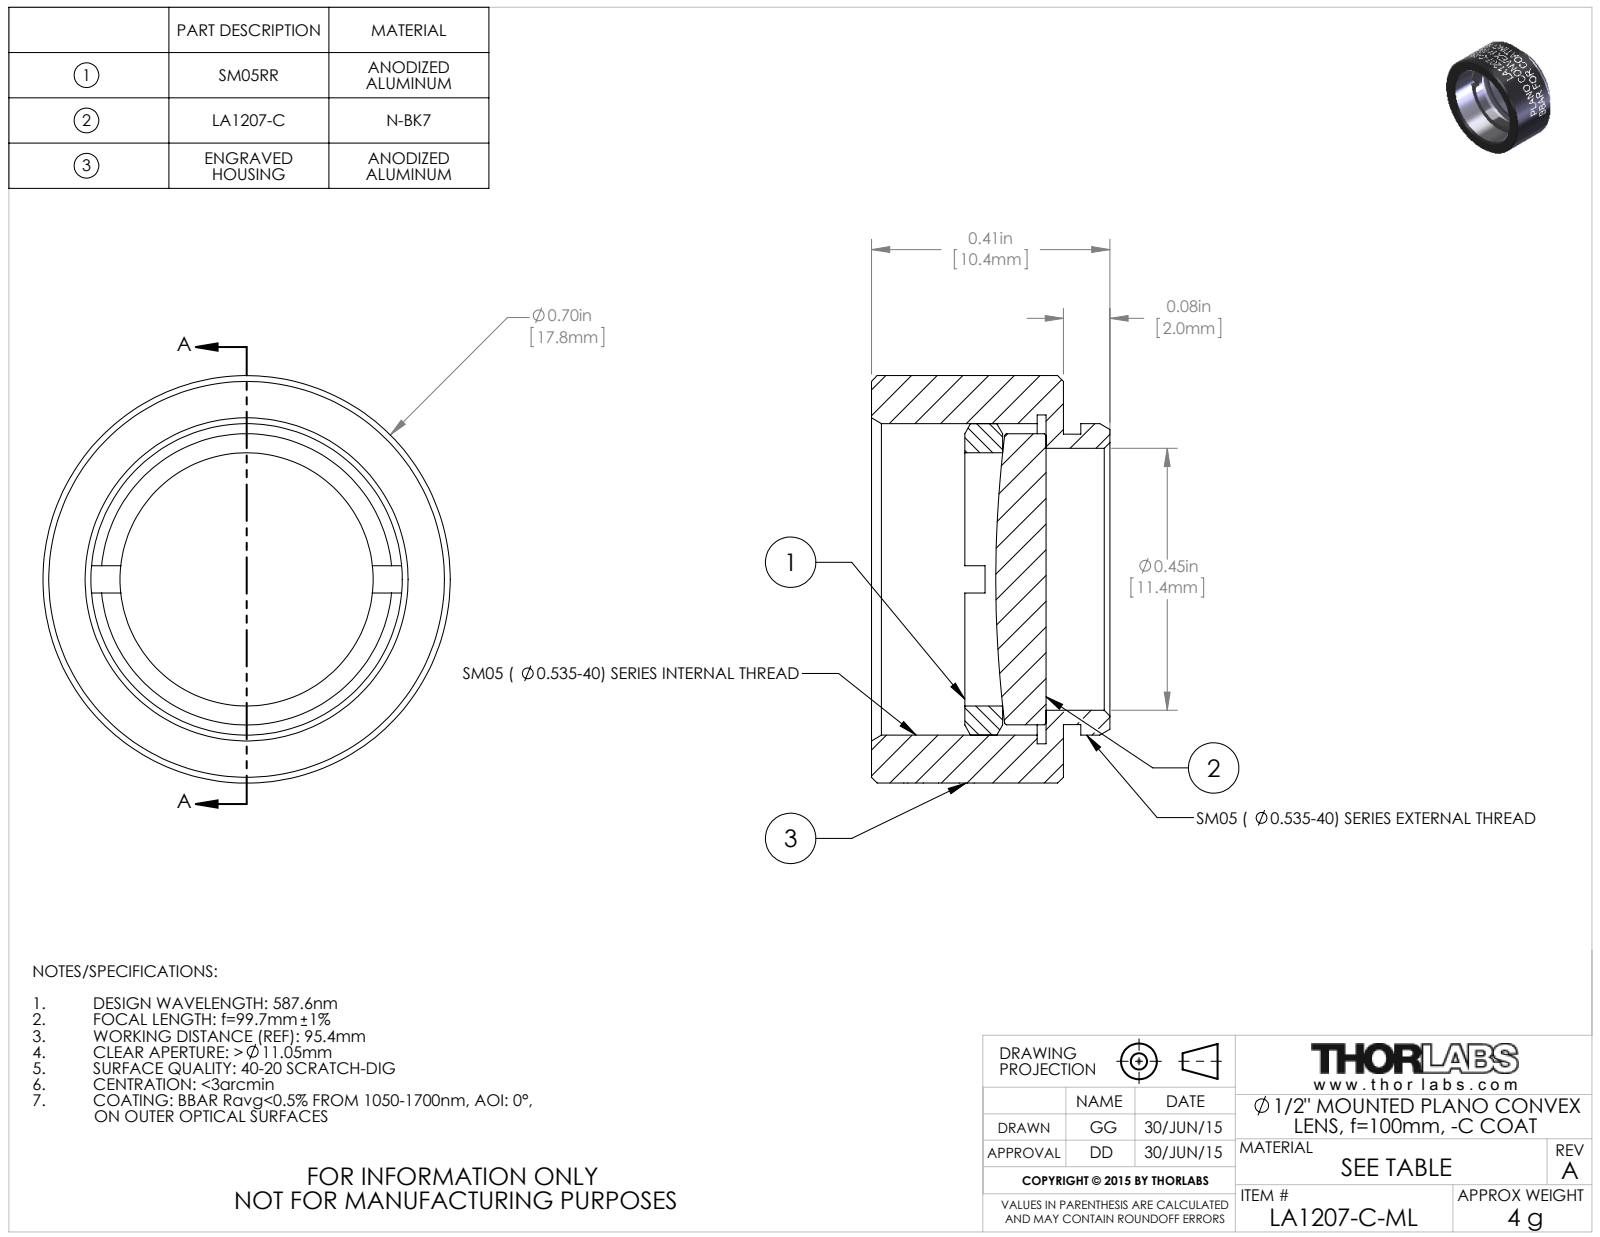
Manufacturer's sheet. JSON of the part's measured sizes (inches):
{"part_name": "TTN039529-E0W", "step_written_by": "SolidWorks 2014 (CONFIG_CONTROL_DESIGN)", "units": "inches", "bodies": {"solids": 3, "faces": 153, "planar": 16, "cylindrical": 116, "other": 21}, "overall_size": [0.7, 0.7, 0.41], "volume_in3": 0.078, "surface_area_in2": 2.847, "round_holes": [[0.435, 1], [0.45, 1], [0.535, 1], [0.565, 1]], "round_bosses_or_shafts": [[0.7, 1], [0.535, 1], [0.5, 1], [0.499, 1]], "face_to_face_distances": [0.03, 0.33, 0.3, 0.105, 0.074, 0.226, 0.17, 0.139, 0.065, 0.161]}
